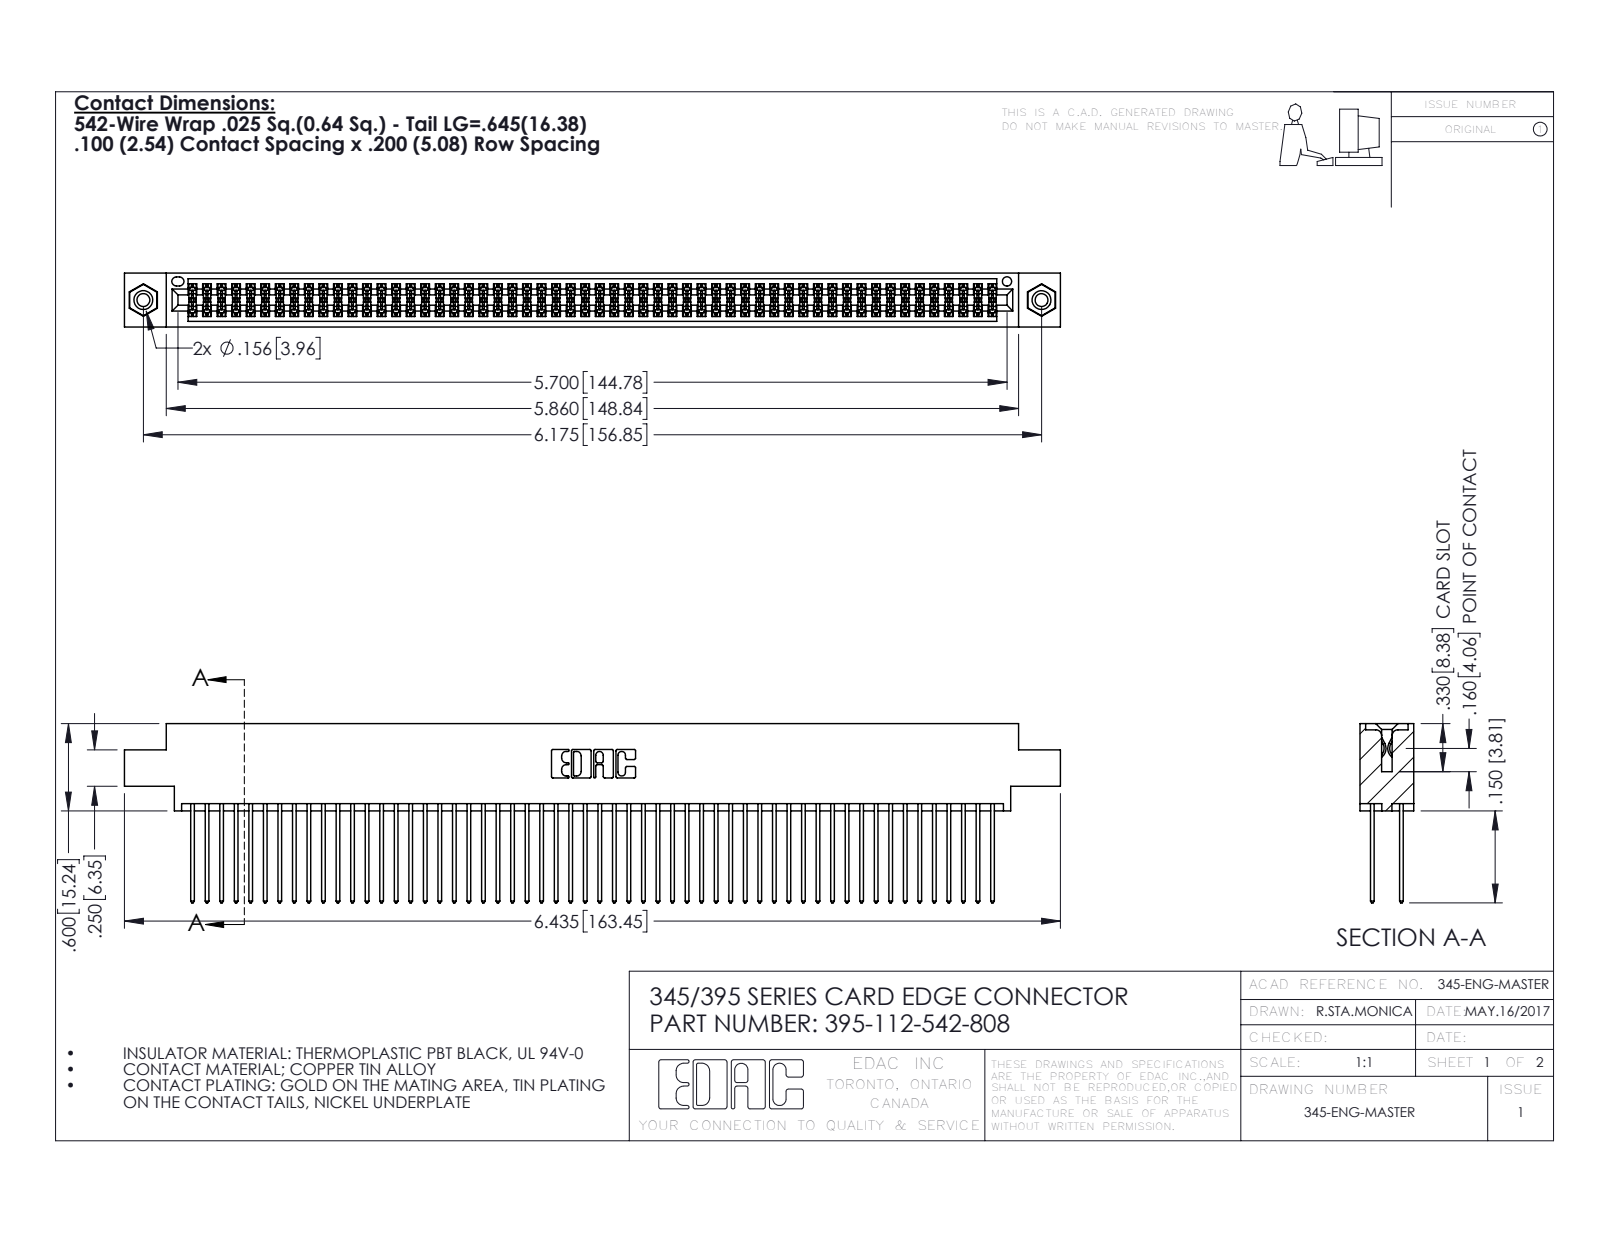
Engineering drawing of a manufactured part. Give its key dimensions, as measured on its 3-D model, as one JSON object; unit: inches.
{"part_name": "345-250-001_345-250-003-102; 345-292-001_345-293-142; 395-112-542-808; 345 Part_0.170 Offset - 0.156 Dia-TI", "step_written_by": "SolidWorks 2016 (CONFIG_CONTROL_DESIGN)", "units": "inches", "bodies": {"solids": 115, "faces": 5790, "planar": 3812, "cylindrical": 1962, "other": 16}, "overall_size": [6.435, 1.232, 0.37], "volume_in3": 1.001, "surface_area_in2": 42.04, "round_holes": [[0.089, 2], [0.125, 2], [0.156, 2], [0.064, 1]], "round_bosses_or_shafts": [[0.155, 2]], "partial_cylinders_radius": [[0.006, 168], [0.01, 112], [0.01, 22], [0.007, 6], [0.031, 6], [0.026, 3], [0.014, 2], [0.019, 2]], "face_to_face_distances": [0.072, 0.298, 0.2, 0.098, 0.272, 0.025, 0.37, 0.225, 0.175, 0.149], "hole_center_spacings": [0.27, 5.939, 6.175]}
